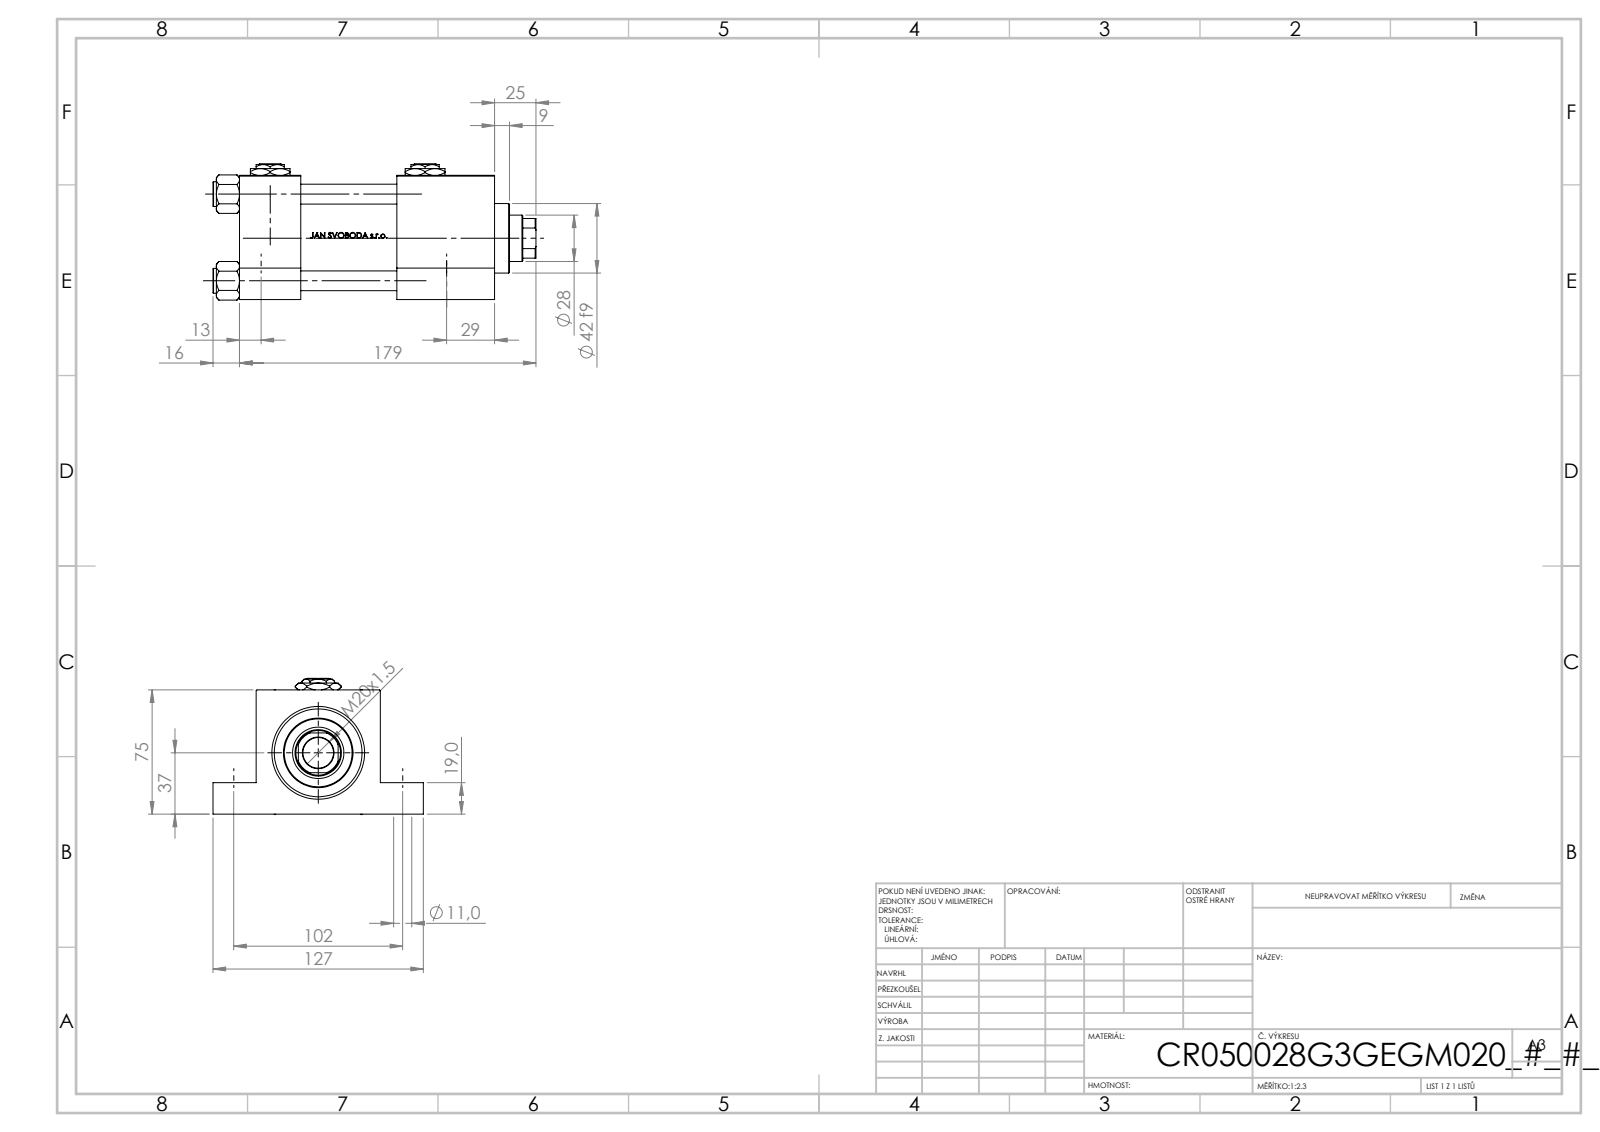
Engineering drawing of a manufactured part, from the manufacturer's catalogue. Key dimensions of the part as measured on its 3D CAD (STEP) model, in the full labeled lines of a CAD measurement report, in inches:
Part name (STEP PRODUCT): V215_VC_A; V215CR_G_TYCINKA; V215CR_G_Body; Zatka_pro_OIL_PORT (+2 more)
STEP written by: SolidWorks 2019 (CONFIG_CONTROL_DESIGN)
Units: inches
Bodies: 13 solids, 1172 faces (476 planar, 124 cylindrical, 572 other)
Overall size (bounding box): 7.677 × 5 × 3.239
Volume: 47.19 in³ · Surface area: 257.2 in²
Round holes (diameter × count): ⌀0.472 ×4, ⌀0.433 ×3, ⌀0.276 ×2, ⌀0.825 ×2, ⌀1.181 ×2, ⌀0.433 ×1, ⌀0.728 ×1, ⌀1.102 ×1, ⌀1.22 ×1, ⌀1.614 ×1, ⌀1.969 ×1, ⌀2.087 ×1
Round bosses / shafts (diameter × count): ⌀0.591 ×4, ⌀2.205 ×1, ⌀1.654 ×1
Partial cylindrical surfaces — rounded edges, fillets, slot ends (radius × count): R0.531 ×1
Main face-to-face distances: 2.953, 1.457, 6.063, 4.606, 0.748, 2.205, 3.74, 2.283, 2.323, 1.024
Hole centre spacings: 2.059, 1.442, 1.47, 2.02, 2.072, 2.912, 4.016, 4.384
